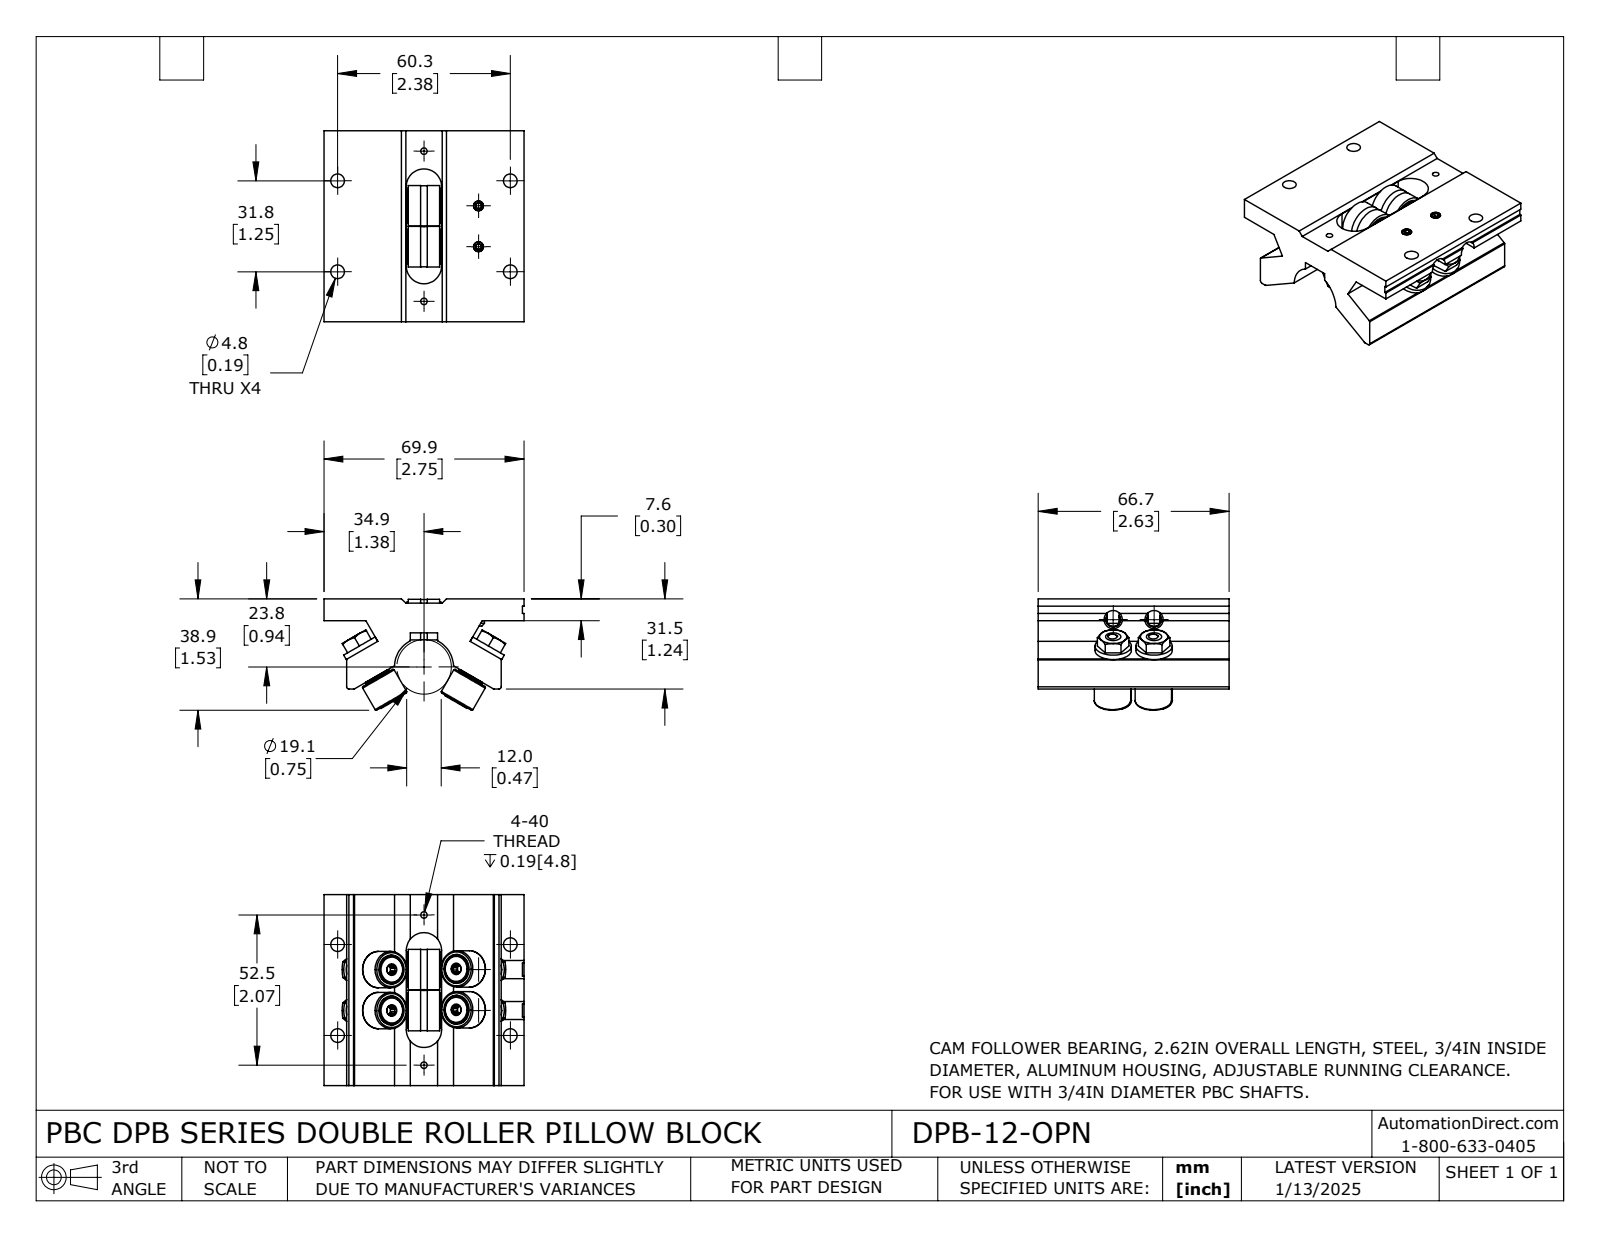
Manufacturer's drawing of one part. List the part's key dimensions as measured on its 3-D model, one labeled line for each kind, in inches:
Part name (STEP PRODUCT): DPB-12-OPN
STEP written by: SolidWorks 2023 (CONFIG_CONTROL_DESIGN)
Units: inches
Bodies: 17 solids, 556 faces (221 planar, 175 cylindrical, 160 other)
Overall size (bounding box): 2.75 × 2.625 × 1.531
Volume: 4.903 in³ · Surface area: 47.42 in²
Round holes (diameter × count): ⌀0.129 ×4, ⌀0.149 ×4, ⌀0.187 ×4, ⌀0.399 ×4, ⌀0.089 ×2, ⌀0.136 ×2, ⌀0.156 ×2, ⌀0.19 ×2, ⌀0.193 ×2, ⌀0.196 ×2, ⌀0.197 ×2, ⌀0.2 ×2
Round bosses / shafts (diameter × count): ⌀0.5 ×6, ⌀0.369 ×4, ⌀0.557 ×2, ⌀0.478 ×2, ⌀0.25 ×2, ⌀0.2 ×2, ⌀0.197 ×2, ⌀0.19 ×2
Partial cylindrical surfaces — rounded edges, fillets, slot ends (radius × count): R0.03 ×4, R0.016 ×2, R0.242 ×1, R0.243 ×1, R0.406 ×1
Main face-to-face distances: 0.405, 0.3, 2.625, 0.312, 2.437, 0.82, 1.305, 1.132, 1.617, 2.125
Hole centre spacings: 0.562, 1.256, 2.039, 1.062, 1.513, 1.968, 2.139, 2.375
